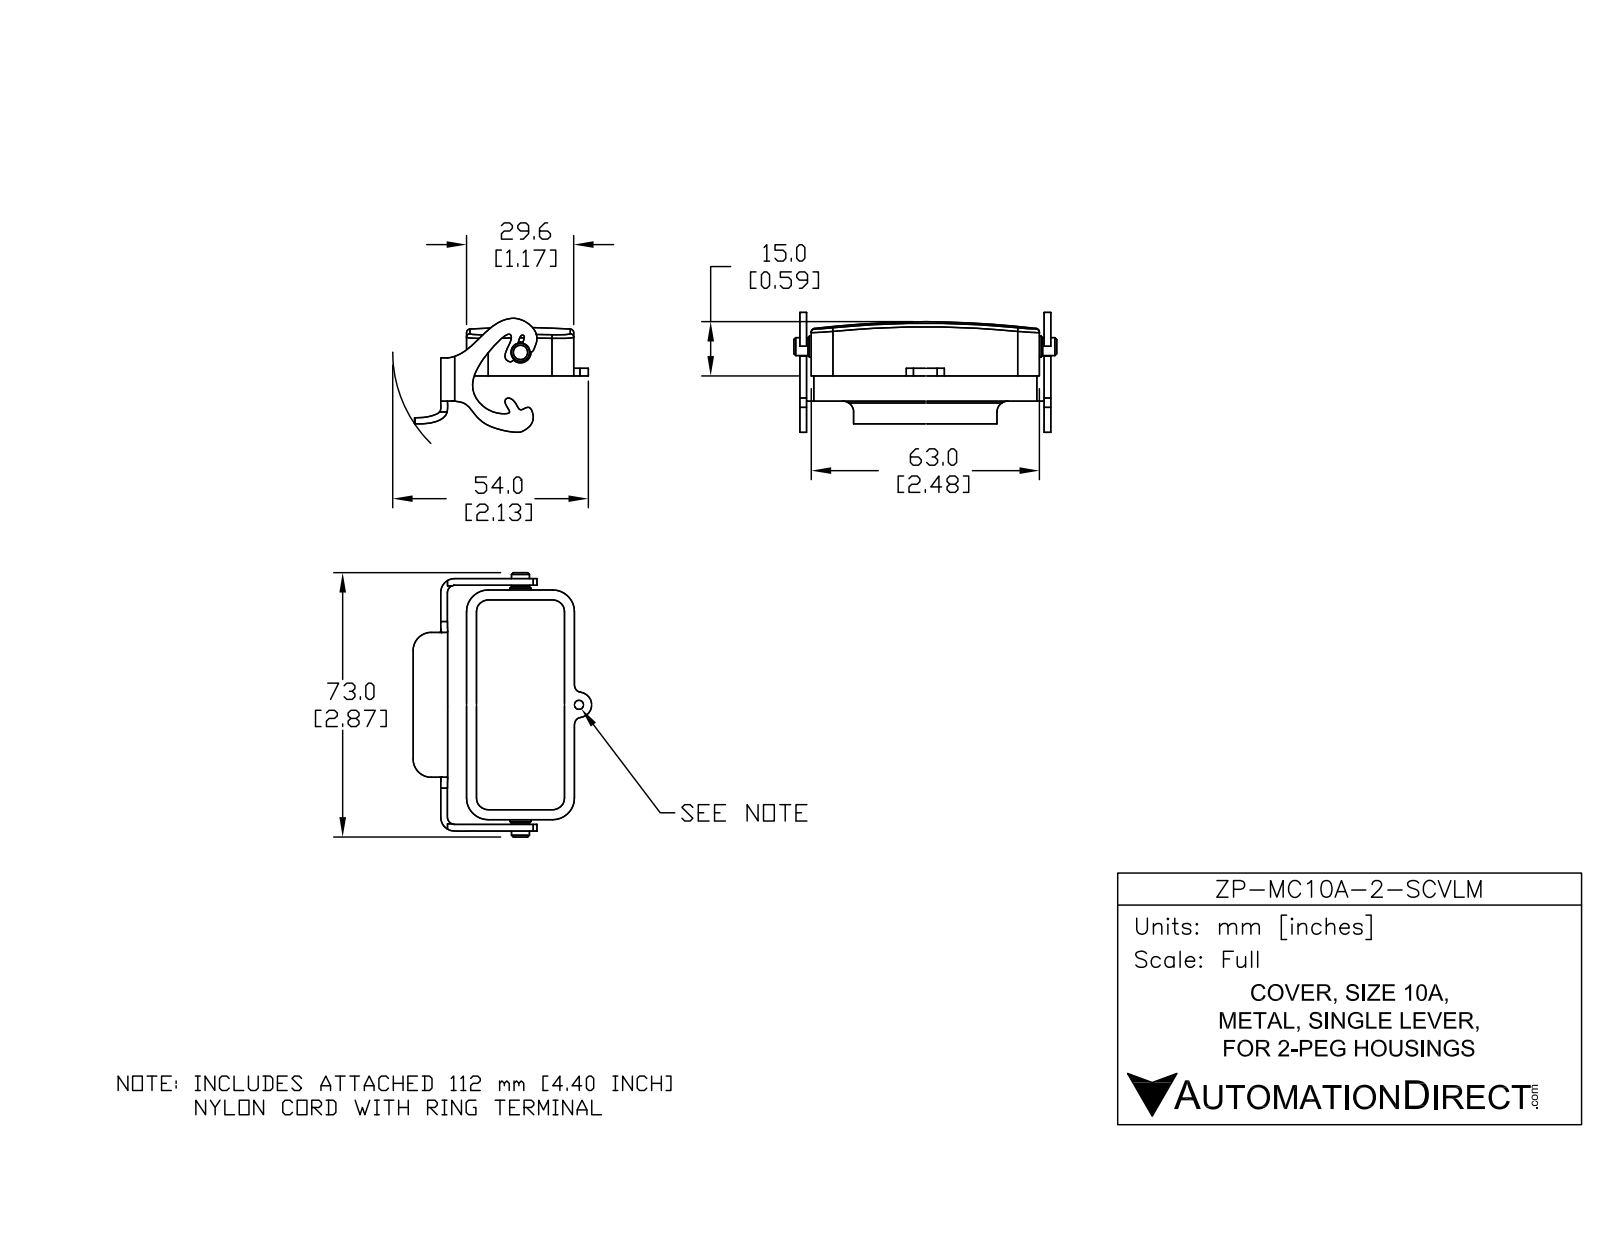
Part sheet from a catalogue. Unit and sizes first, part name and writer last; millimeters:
Units: millimetres
Overall size (bounding box): 151.66 × 77.18 × 65.03
Round holes (diameter × count): ⌀2.5 ×1, ⌀4.1 ×1
Round bosses / shafts (diameter × count): ⌀5.77 ×1, ⌀4.95 ×1
Partial cylindrical surfaces — rounded edges, fillets, slot ends (radius × count): R6 ×6, R0.45 ×4, R2 ×4, R3.25 ×4, R0.6 ×2, R3 ×2, R3.85 ×2, R5 ×2
Main face-to-face distances: 2.75, 1.85, 27.05, 7.13, 5.28, 36.93, 35.08, 29.8, 34.18, 32.33
Volume: 16 028 mm³ · Surface area: 13 347 mm²
Bodies: 5 solids, 127 faces (49 planar, 46 cylindrical, 32 other)
Part name (STEP PRODUCT): ZP-MC10A-2-SCVLM
STEP written by: SolidWorks 2014 (AUTOMOTIVE_DESIGN)
